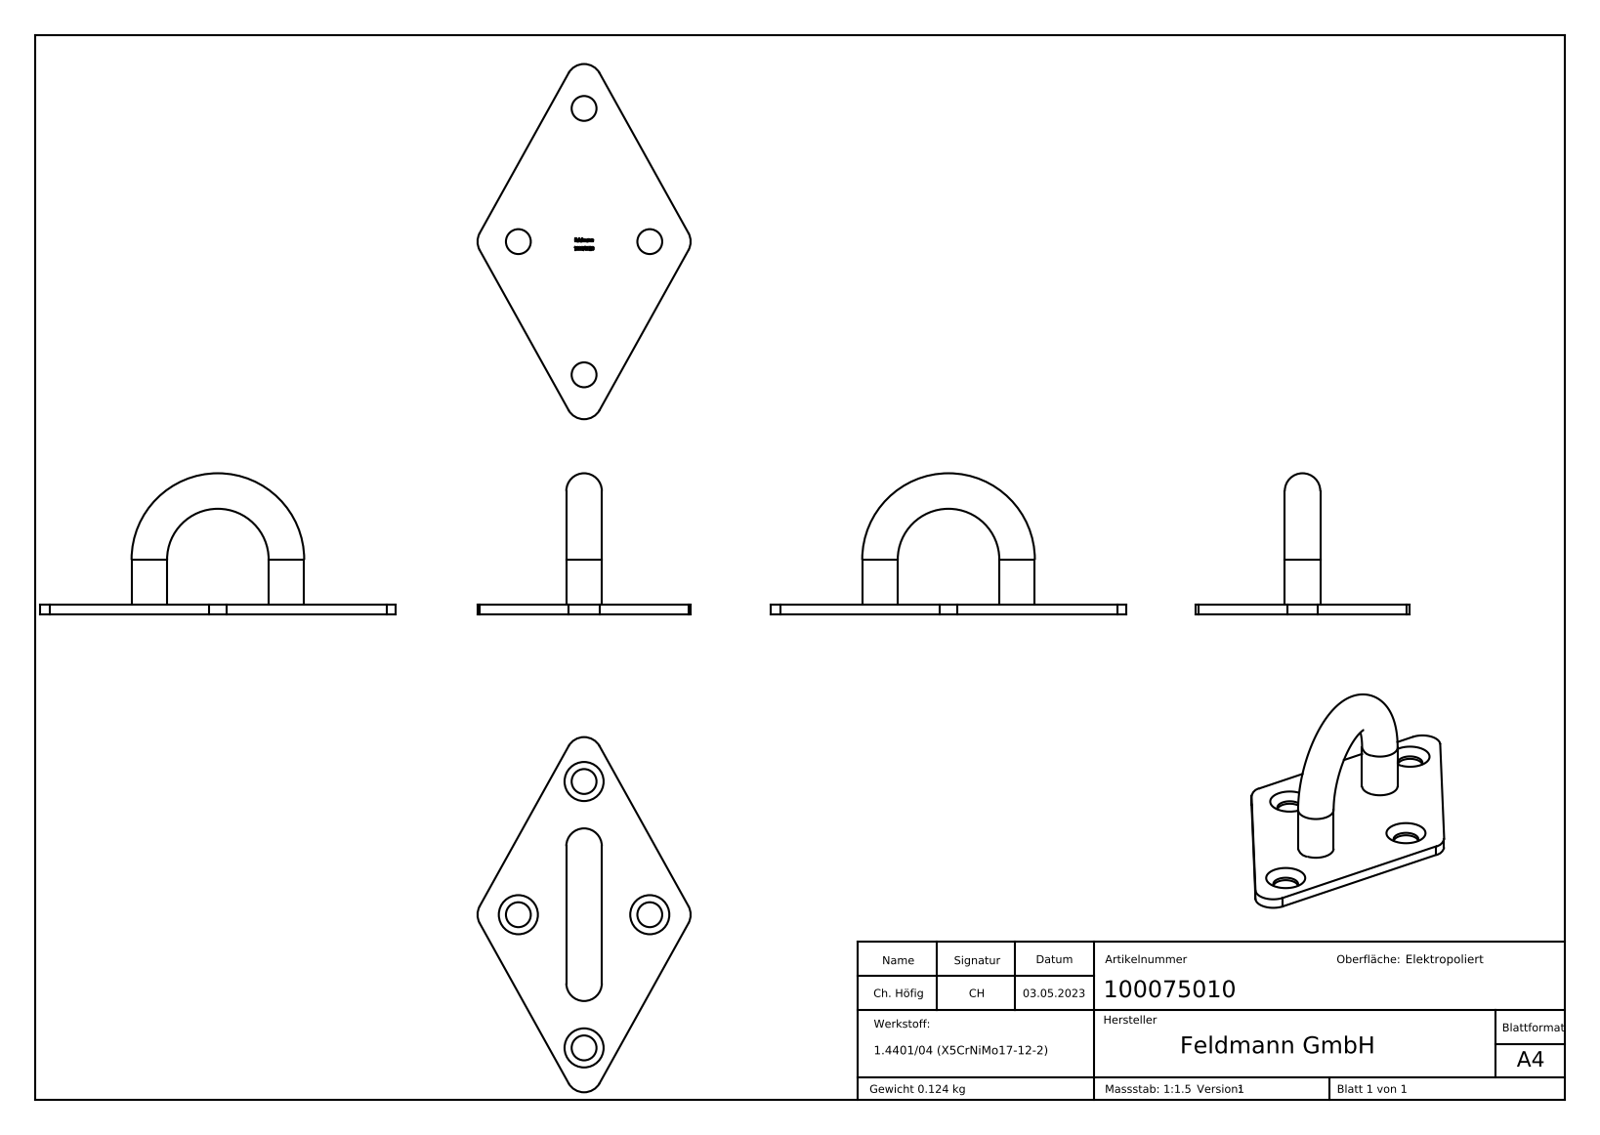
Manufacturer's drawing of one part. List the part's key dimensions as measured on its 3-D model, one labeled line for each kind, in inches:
Part name (STEP PRODUCT): 100075010
STEP written by: SolidWorks 2018 (CONFIG_CONTROL_DESIGN)
Units: inches
Bodies: 1 solid, 225 faces (109 planar, 10 cylindrical, 106 other)
Overall size (bounding box): 3.937 × 2.362 × 1.567
Volume: 0.947 in³ · Surface area: 15.17 in²
Round holes (diameter × count): ⌀0.276 ×4
Round bosses / shafts (diameter × count): ⌀0.394 ×2
Partial cylindrical surfaces — rounded edges, fillets, slot ends (radius × count): R0.197 ×4
Main face-to-face distances: 0.11, 2.115, 0.106, 0.07, 0.074, 0.033, 0.083, 0.039, 0.044, 0.168
Hole centre spacings: 1.646, 1.457, 2.953
